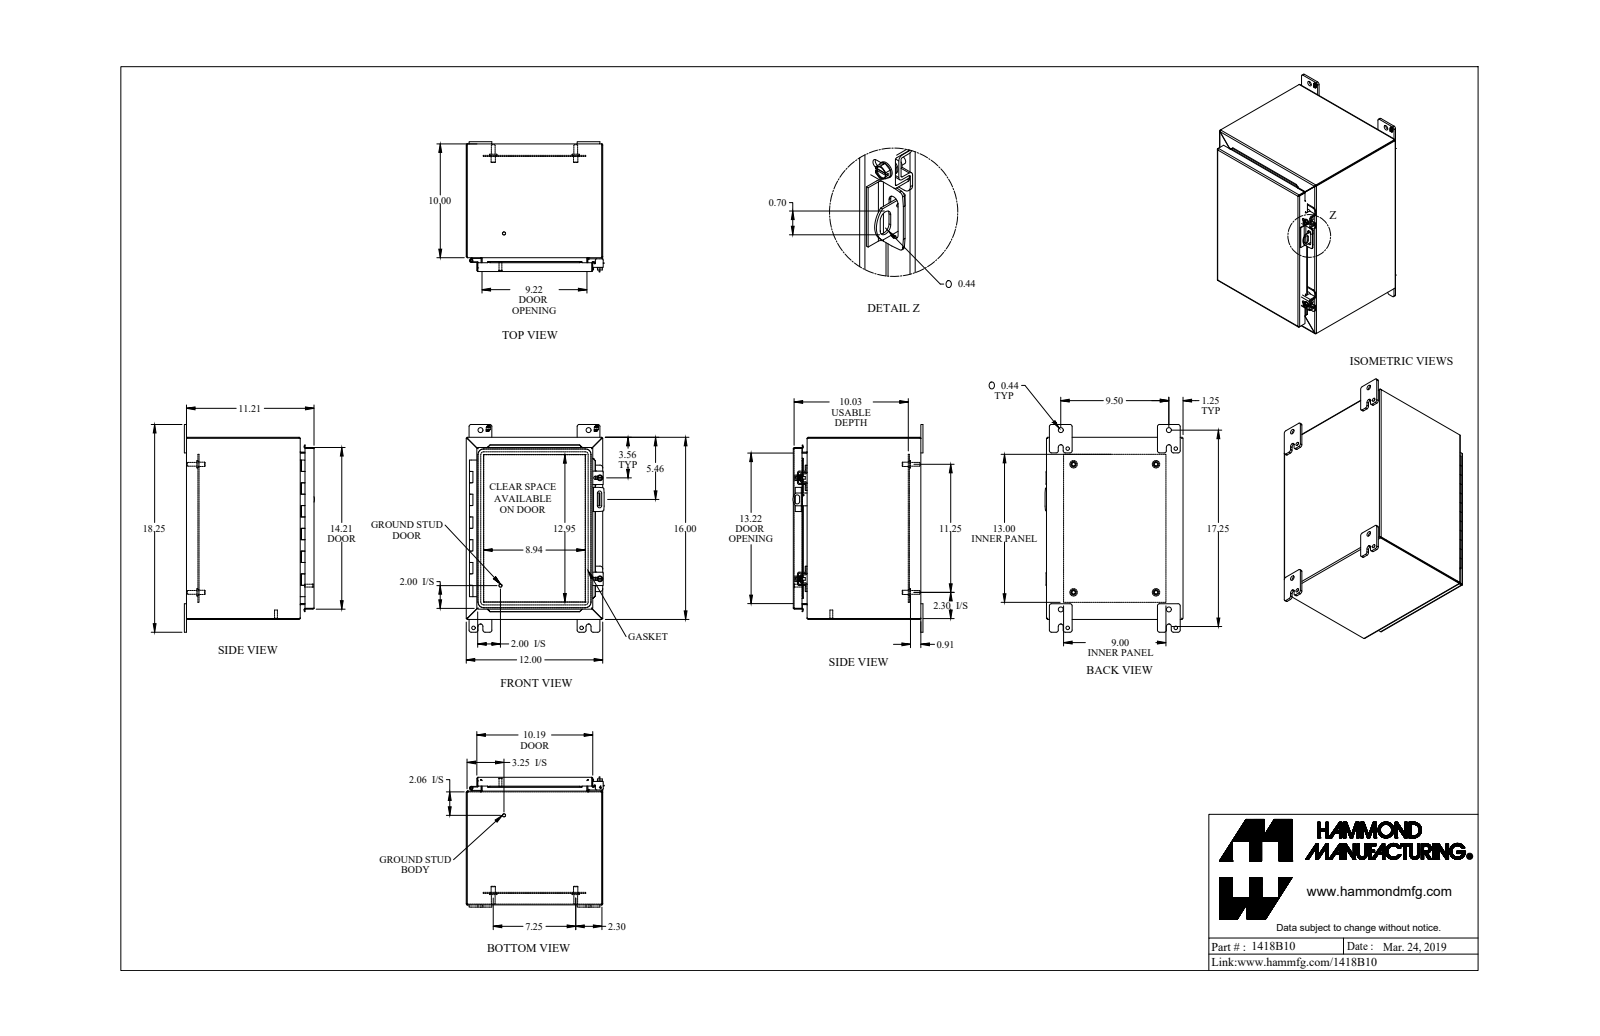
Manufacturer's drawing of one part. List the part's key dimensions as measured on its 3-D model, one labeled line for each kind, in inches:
Part name (STEP PRODUCT): 1418B10
STEP written by: SolidWorks 2019 (AUTOMOTIVE_DESIGN)
Units: inches
Bodies: 37 solids, 894 faces (633 planar, 219 cylindrical, 42 other)
Overall size (bounding box): 18.25 × 12.125 × 11.437
Volume: 196.3 in³ · Surface area: 2 528 in²
Round holes (diameter × count): ⌀0.313 ×4, ⌀0.437 ×4, ⌀0.5 ×4, ⌀0.213 ×2, ⌀0.265 ×2, ⌀0.307 ×2, ⌀0.375 ×2, ⌀0.445 ×2, ⌀0.125 ×1, ⌀0.187 ×1
Round bosses / shafts (diameter × count): ⌀0.65 ×4, ⌀0.375 ×4, ⌀0.33 ×4, ⌀1 ×2, ⌀0.5 ×2, ⌀0.39 ×2, ⌀0.281 ×2, ⌀0.25 ×2
Partial cylindrical surfaces — rounded edges, fillets, slot ends (radius × count): R0.188 ×26, R0.036 ×16, R0.108 ×16, R0.048 ×13, R0.143 ×13, R0.079 ×8, R0.218 ×8, R0.25 ×8
Main face-to-face distances: 0.072, 11.928, 15.928, 11.113, 11.856, 12, 11.185, 0.767, 10.346, 10.418
Hole centre spacings: 9.5, 18.393, 7.25, 8.508, 10.285, 12.8, 13.384, 1.735
